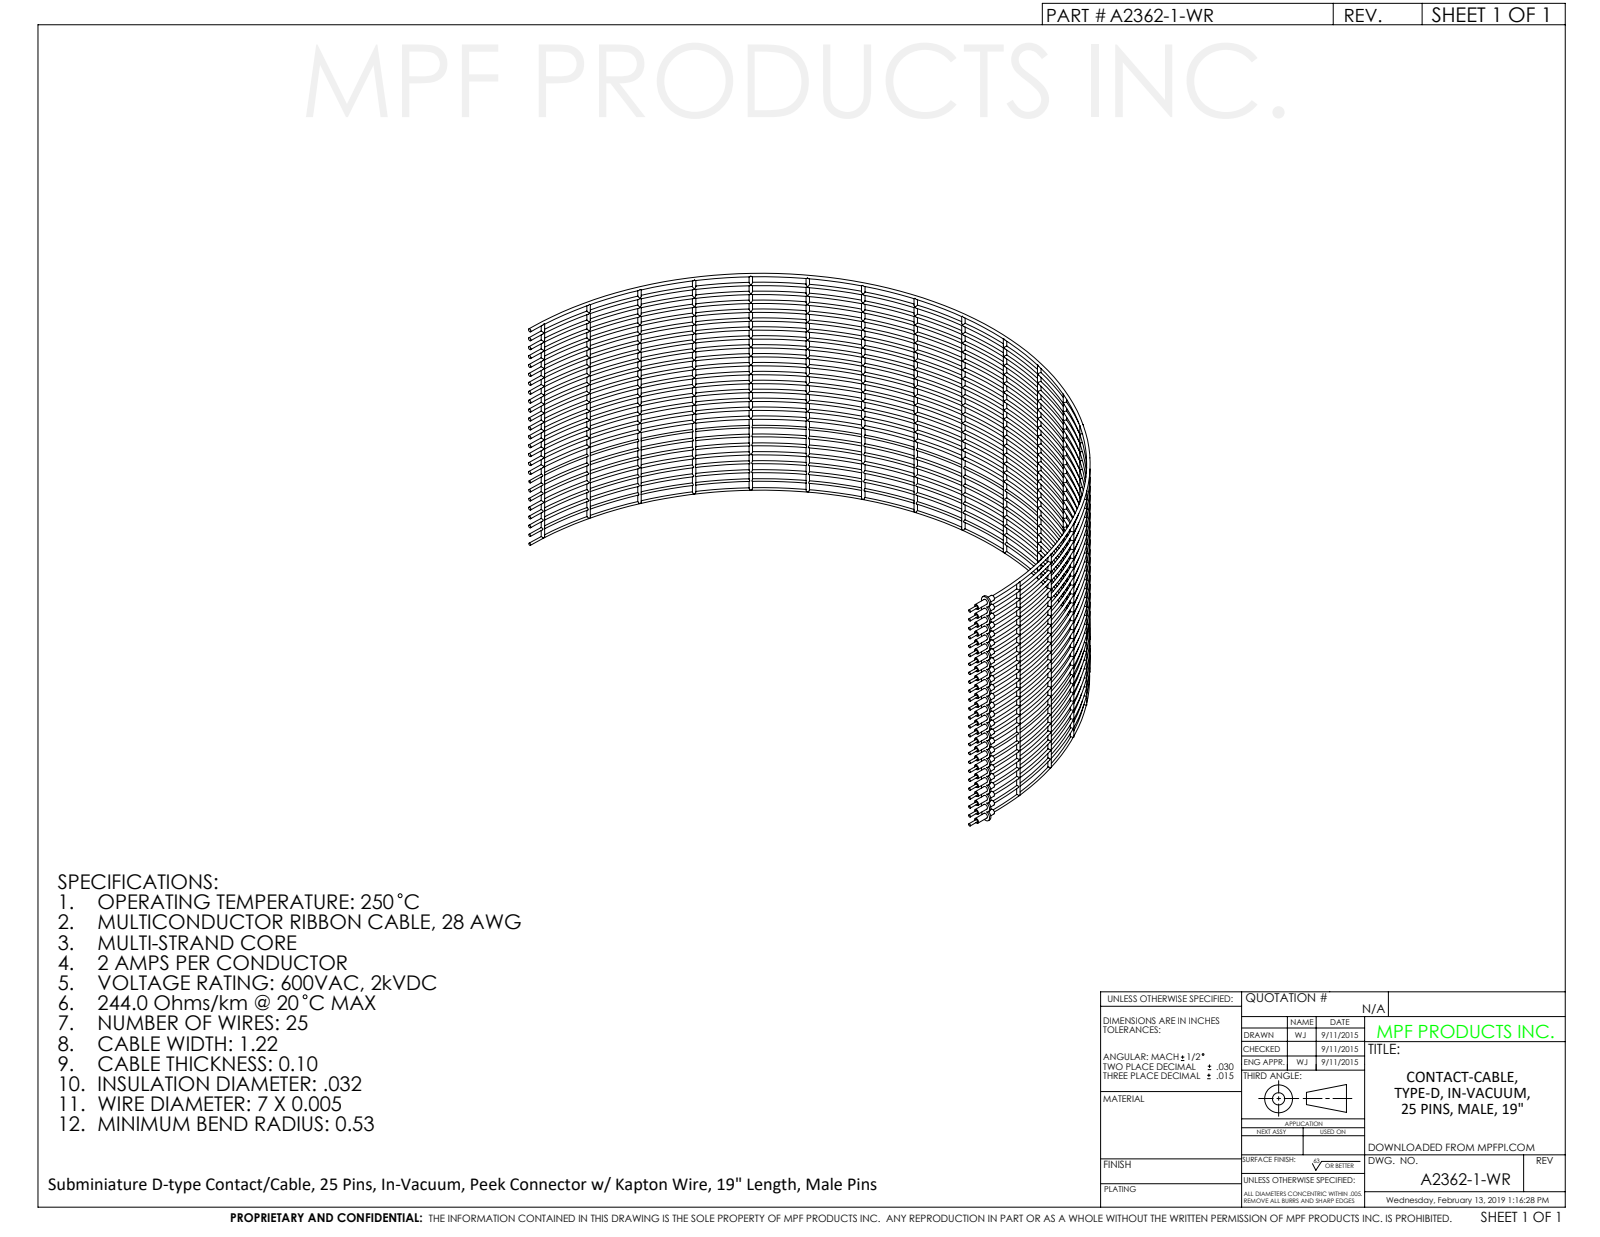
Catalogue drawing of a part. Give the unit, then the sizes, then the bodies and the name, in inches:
Units: inches
Overall size (bounding box): 6.069 × 3.315 × 2.505
Round bosses / shafts (diameter × count): ⌀0.05 ×25, ⌀0.023 ×25, ⌀0.105 ×24, ⌀0.032 ×18
Partial cylindrical surfaces — rounded edges, fillets, slot ends (radius × count): R0.053 ×1
Main face-to-face distances: 0.018, 0.074, 0.091, 0.207, 0.134, 0.116, 0.298, 0.225, 0.207, 0.091
Volume: 0.205 in³ · Surface area: 26.16 in²
Bodies: 1 solid, 1883 faces (139 planar, 816 cylindrical, 928 other)
Part name (STEP PRODUCT): A2362-1-WR
STEP written by: SolidWorks 2012 (CONFIG_CONTROL_DESIGN)
